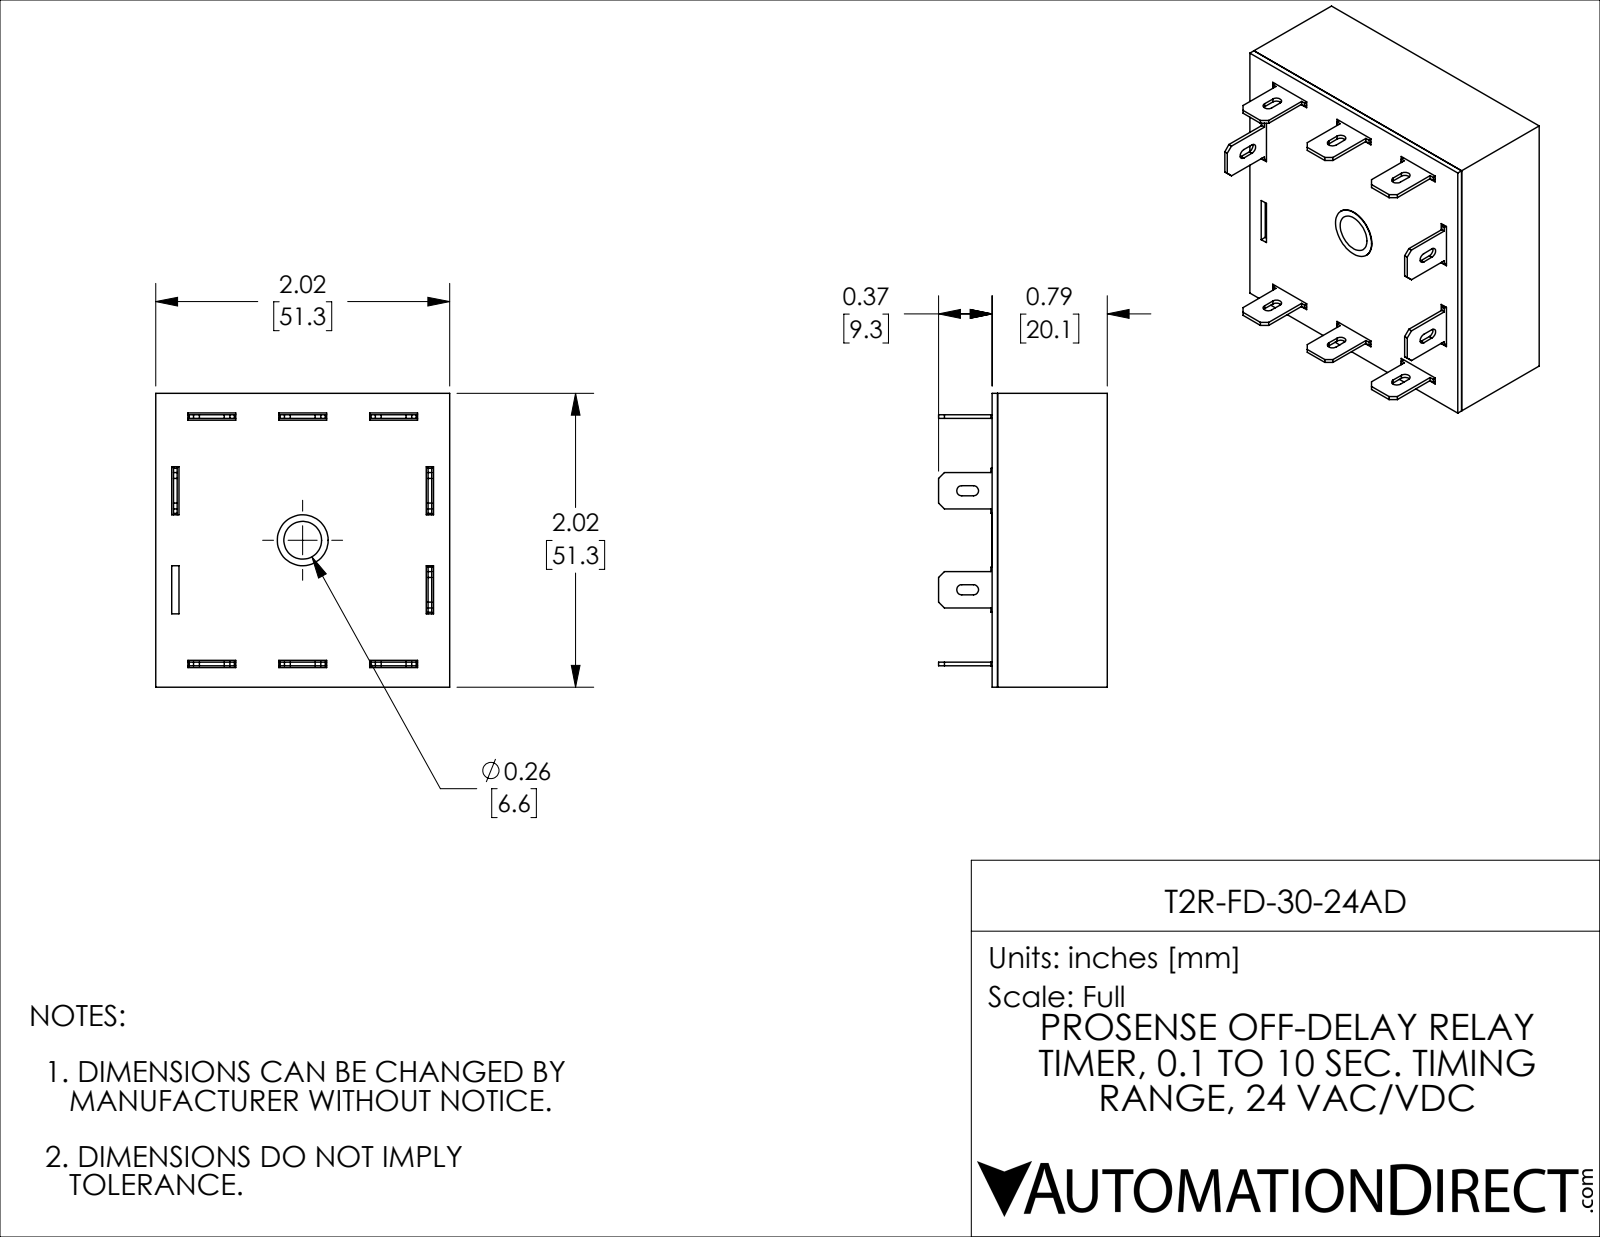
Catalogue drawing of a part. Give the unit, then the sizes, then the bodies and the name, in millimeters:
Units: millimetres
Overall size (bounding box): 51.31 × 51.31 × 29.46
Round holes (diameter × count): ⌀8.89 ×1
Partial cylindrical surfaces — rounded edges, fillets, slot ends (radius × count): R0.89 ×10
Main face-to-face distances: 1.14, 50.16, 19.15, 20.12, 0.97, 18.01, 18.98, 51.3, 3.74, 47.56
Volume: 11 178 mm³ · Surface area: 23 301 mm²
Bodies: 11 solids, 280 faces (256 planar, 22 cylindrical, 2 other)
Part name (STEP PRODUCT): T2R-FD-30-24AD
STEP written by: SolidWorks 2021 (CONFIG_CONTROL_DESIGN)
